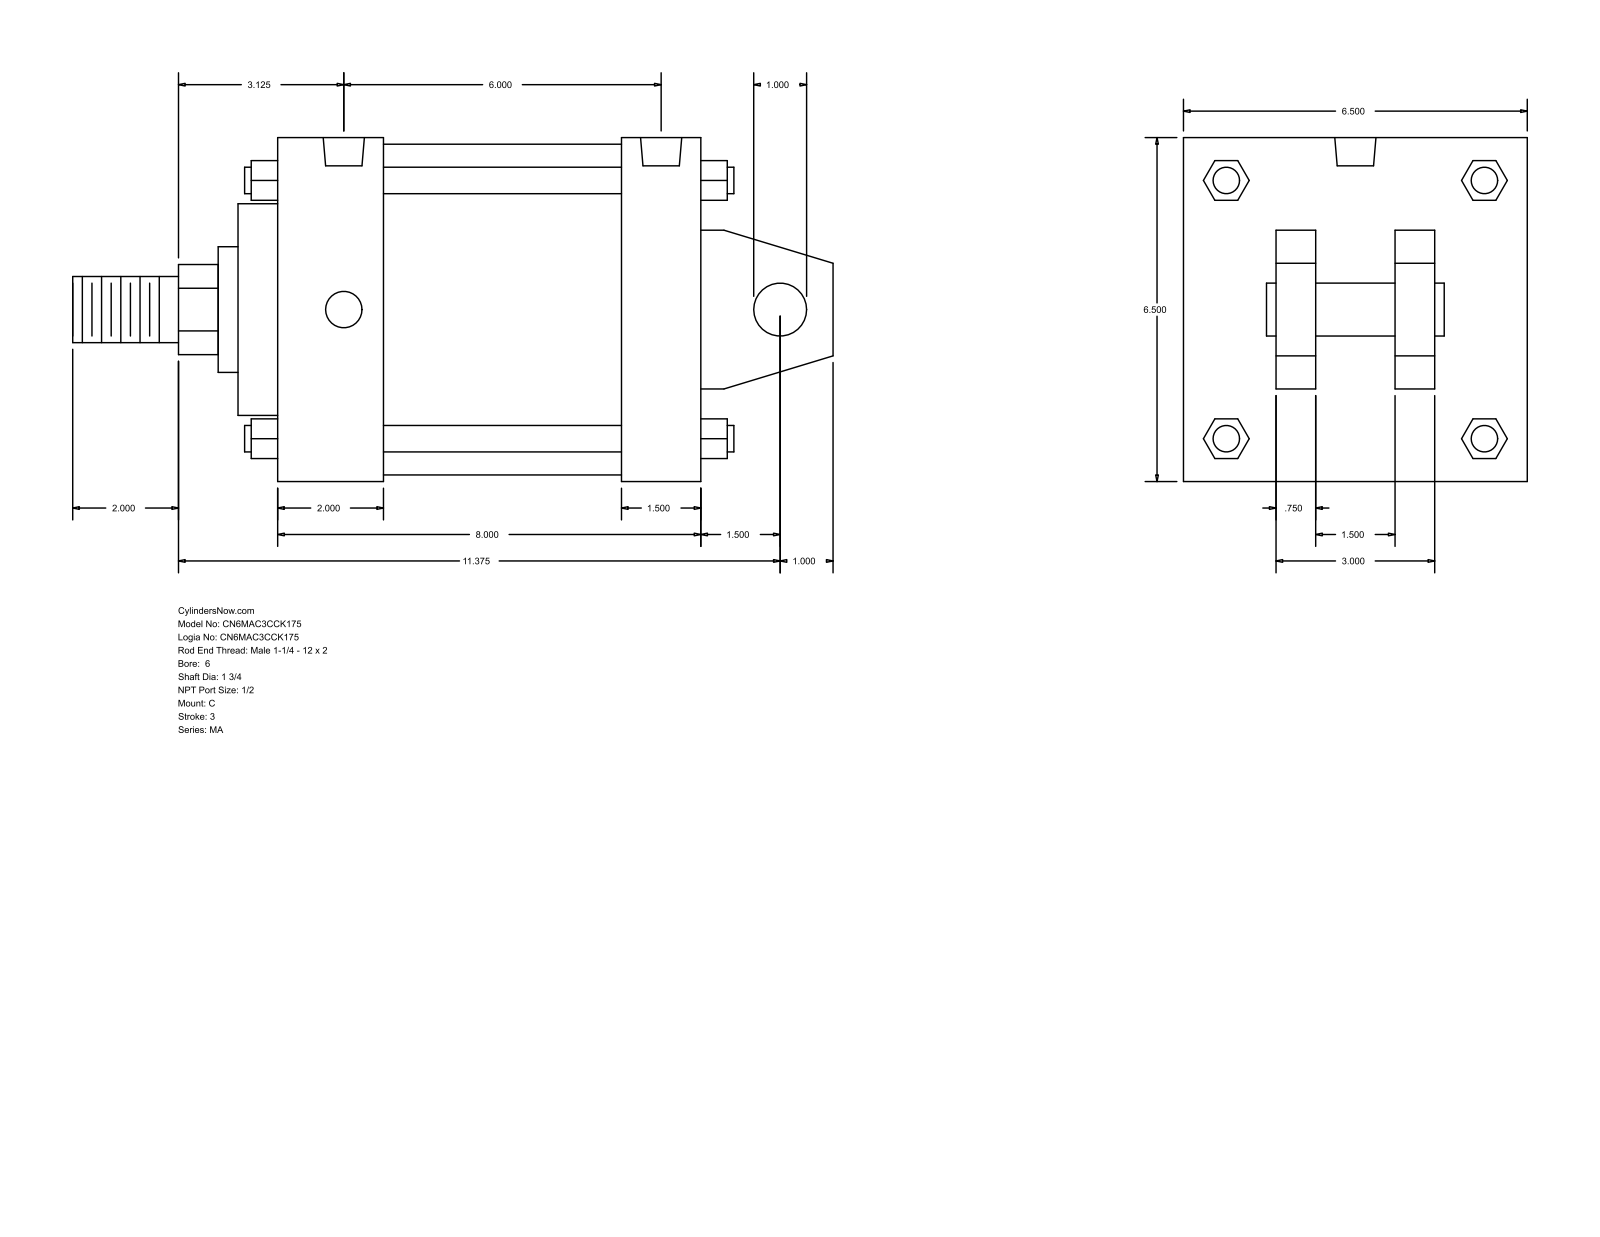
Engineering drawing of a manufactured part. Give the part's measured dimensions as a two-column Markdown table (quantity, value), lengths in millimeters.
| quantity | value |
| --- | --- |
| part name | MA_C__0600_1.75 |
| STEP written by | GSSL Pune (CONFIG_CONTROL_DESIGN) |
| units | millimeters |
| bodies | 0 solids, 141 faces (109 planar, 32 cylindrical, 0 other) |
| overall size | 365.12 × 165.1 × 165.1 |
| round holes (diameter × count) | 17.46 × 4, 19.77 × 2 |
| round bosses / shafts (diameter × count) | 12.7 × 4, 158.75 × 1, 101.6 × 1, 60.33 × 1, 44.45 × 1, 31.75 × 1, 25.4 × 1 |
| partial cylindrical surfaces (radius × count) | 21.63 × 1 |
| main face-to-face distances | 165.1, 203.2, 19.05, 38.1, 63.5, 101.6, 50.8, 120.65, 44.45, 57.15 |
| hole center spacings | 152.4 |
